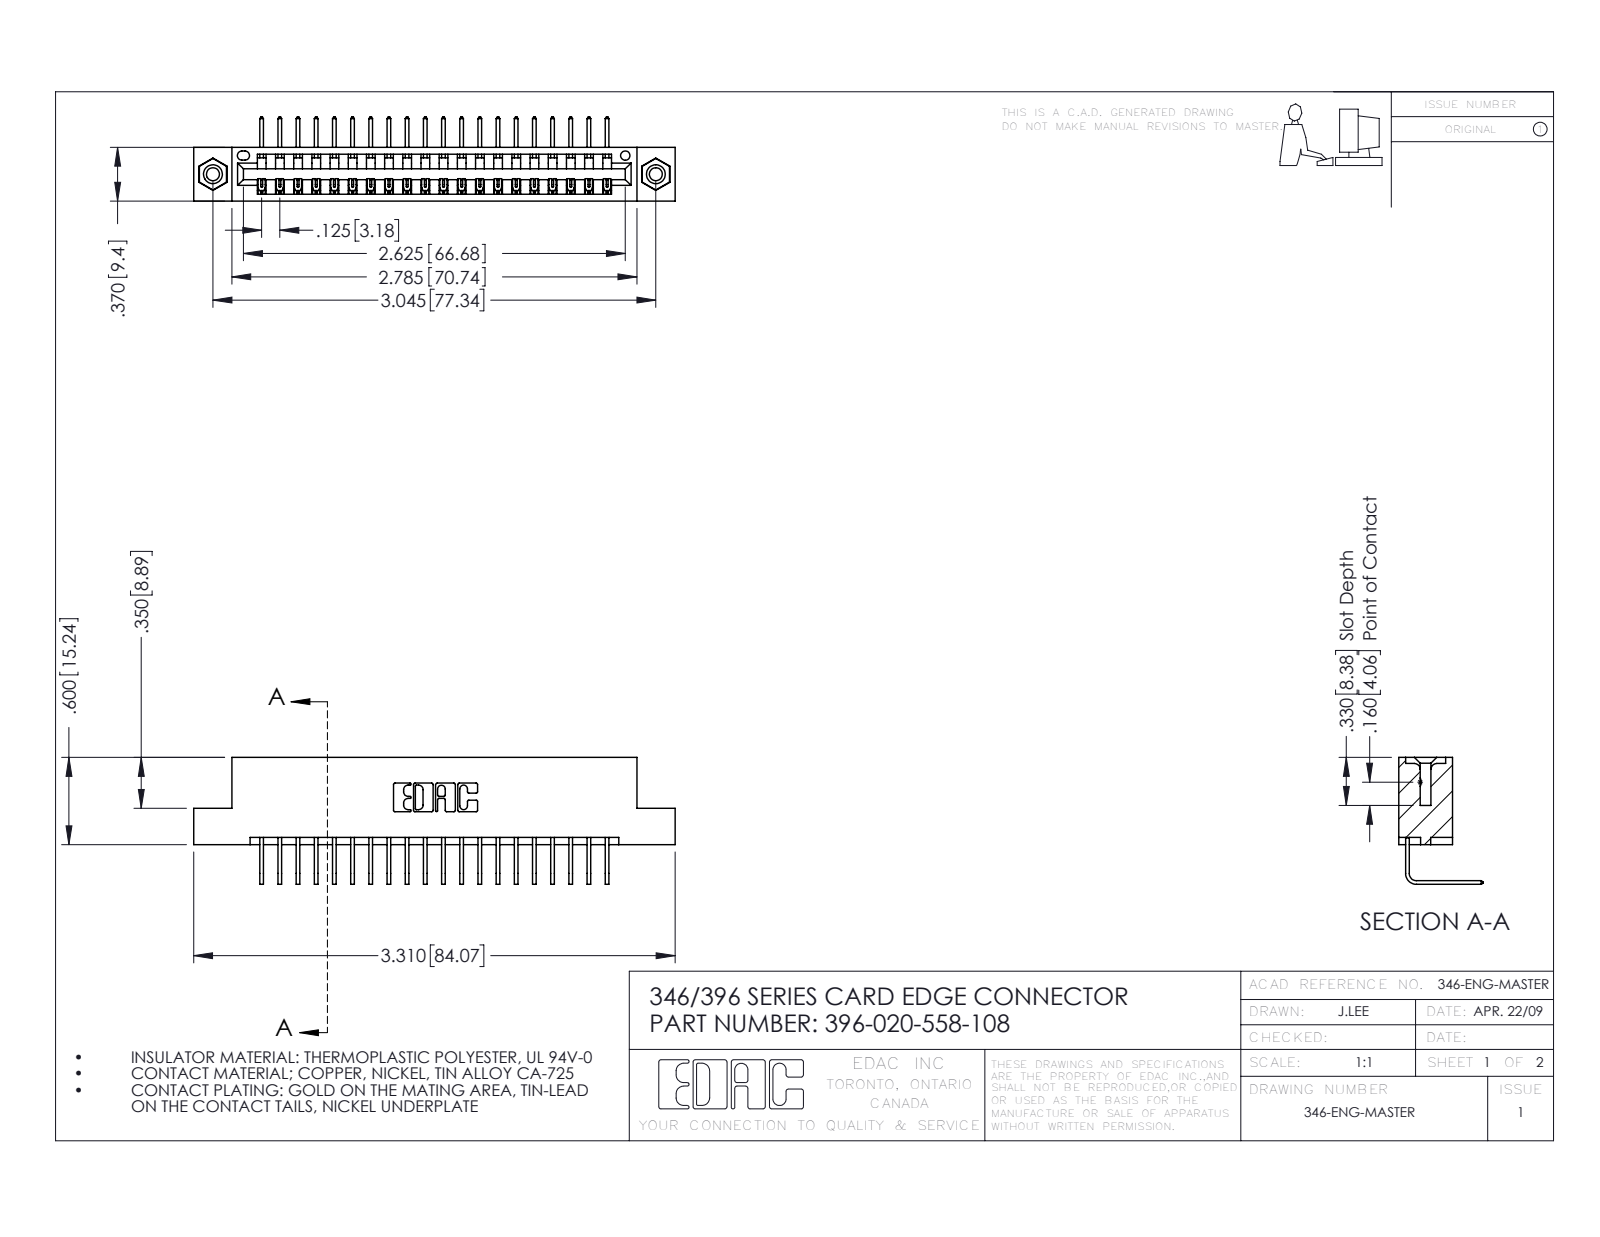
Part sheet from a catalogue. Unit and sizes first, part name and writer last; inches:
Units: inches
Overall size (bounding box): 3.31 × 0.873 × 0.58
Round holes (diameter × count): ⌀0.089 ×2, ⌀0.125 ×2, ⌀0.156 ×2, ⌀0.064 ×1
Round bosses / shafts (diameter × count): ⌀0.155 ×2
Partial cylindrical surfaces — rounded edges, fillets, slot ends (radius × count): R0.006 ×40, R0.01 ×22, R0.007 ×6, R0.031 ×6, R0.026 ×3, R0.031 ×2, R0.04 ×2, R0.014 ×1
Main face-to-face distances: 0.322, 0.048, 0.37, 0.25, 0.298, 0.025, 0.072, 0.148, 0.222, 0.1
Hole centre spacings: 0.246, 2.837, 3.045
Volume: 0.486 in³ · Surface area: 15.7 in²
Bodies: 23 solids, 1382 faces (948 planar, 418 cylindrical, 16 other)
Part name (STEP PRODUCT): 346 Part_Flush Mounting Lugs - 0.156 Dia-TI; 345-292-001_558 Tail - 2; 396-020-558-108; 345-250-001_345-250-003-102
STEP written by: SolidWorks 2016 (CONFIG_CONTROL_DESIGN)
